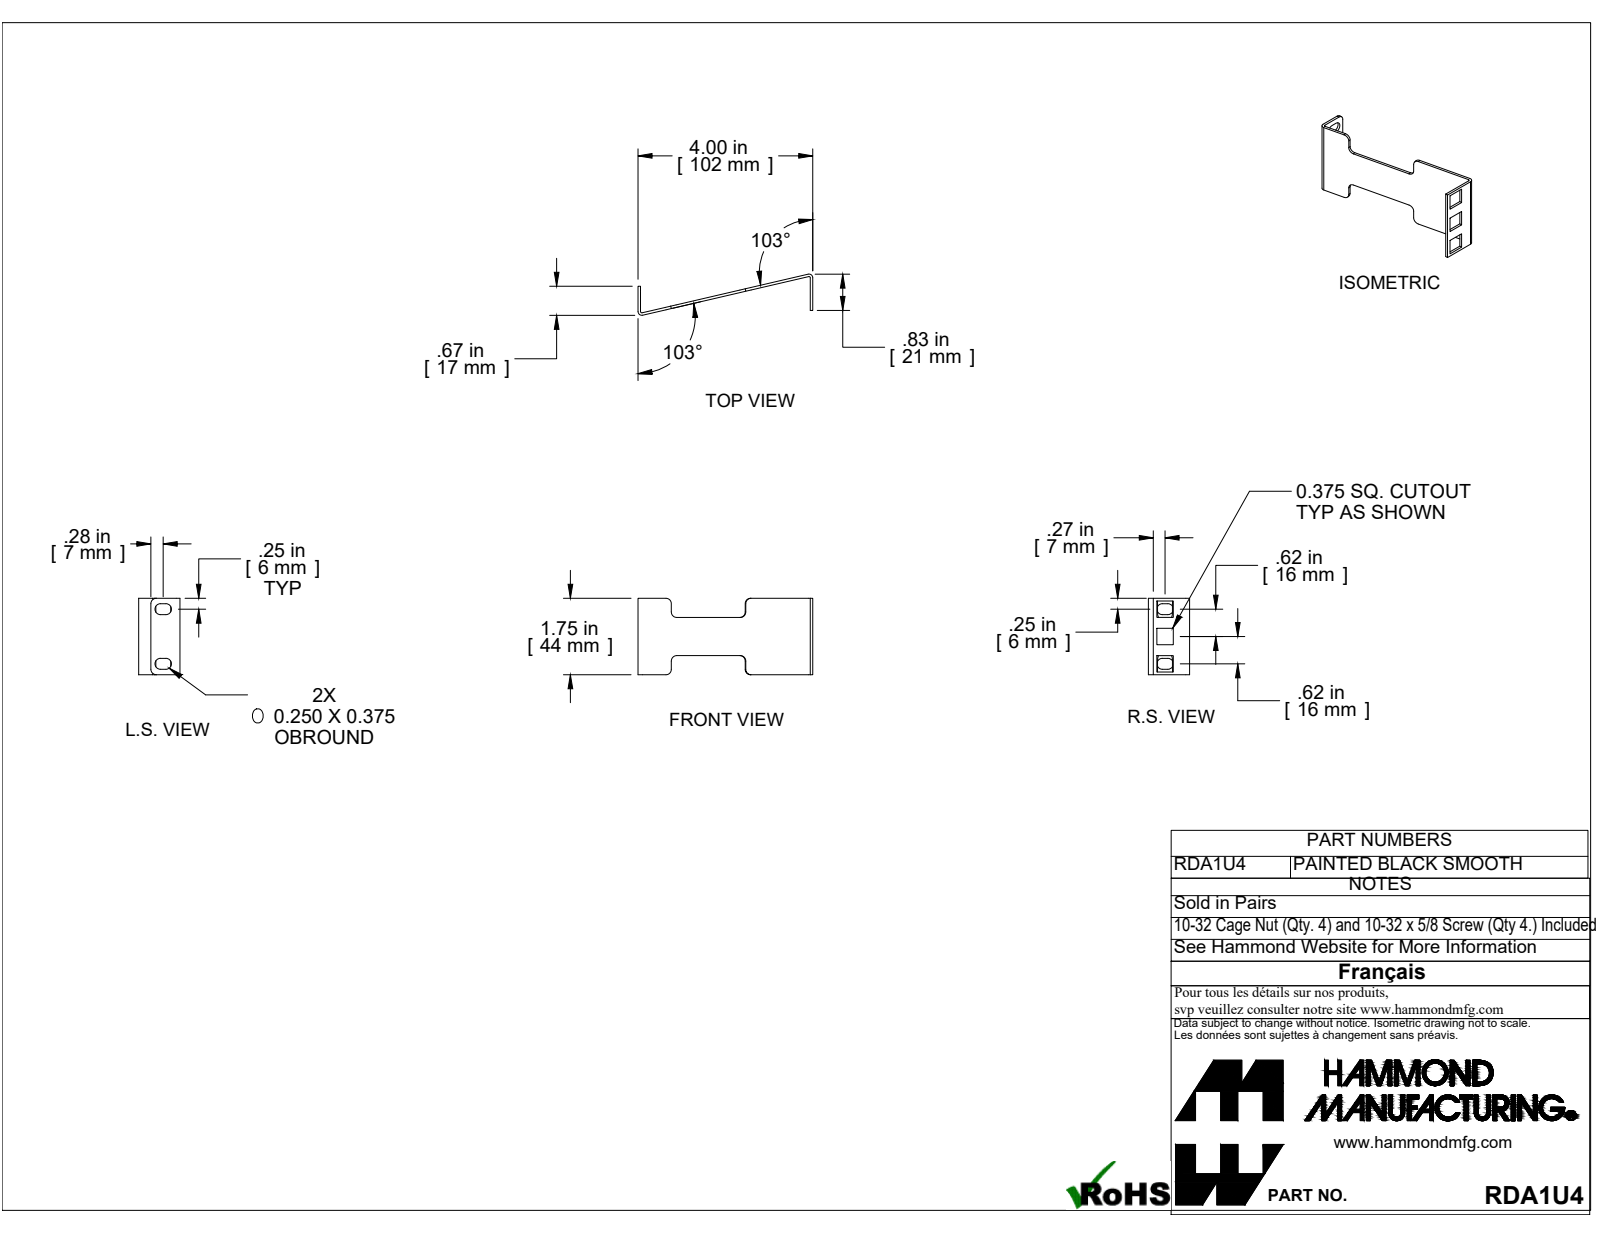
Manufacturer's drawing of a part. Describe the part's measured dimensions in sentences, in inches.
The part is named "RDA1U4". Its 3-D file was written by "SolidWorks 2019 (CONFIG_CONTROL_DESIGN)". It is 1 solid with 52 faces: 34 planar, 18 cylindrical and 0 other. Overall it measures 4 by 1.75 by 0.945 inches. Its volume is 0.421 cubic inches and its surface area 16.04 square inches. Partial cylindrical surfaces (rounded edges, fillets, slot ends): 14 of radius 0.125, 2 of radius 0.029, 2 of radius 0.086. The main face-to-face distances are 0.057, 3.943, 4, 3.886, 1.75, 0.438, 1.312, 0.375, 0.553, 0.874.
